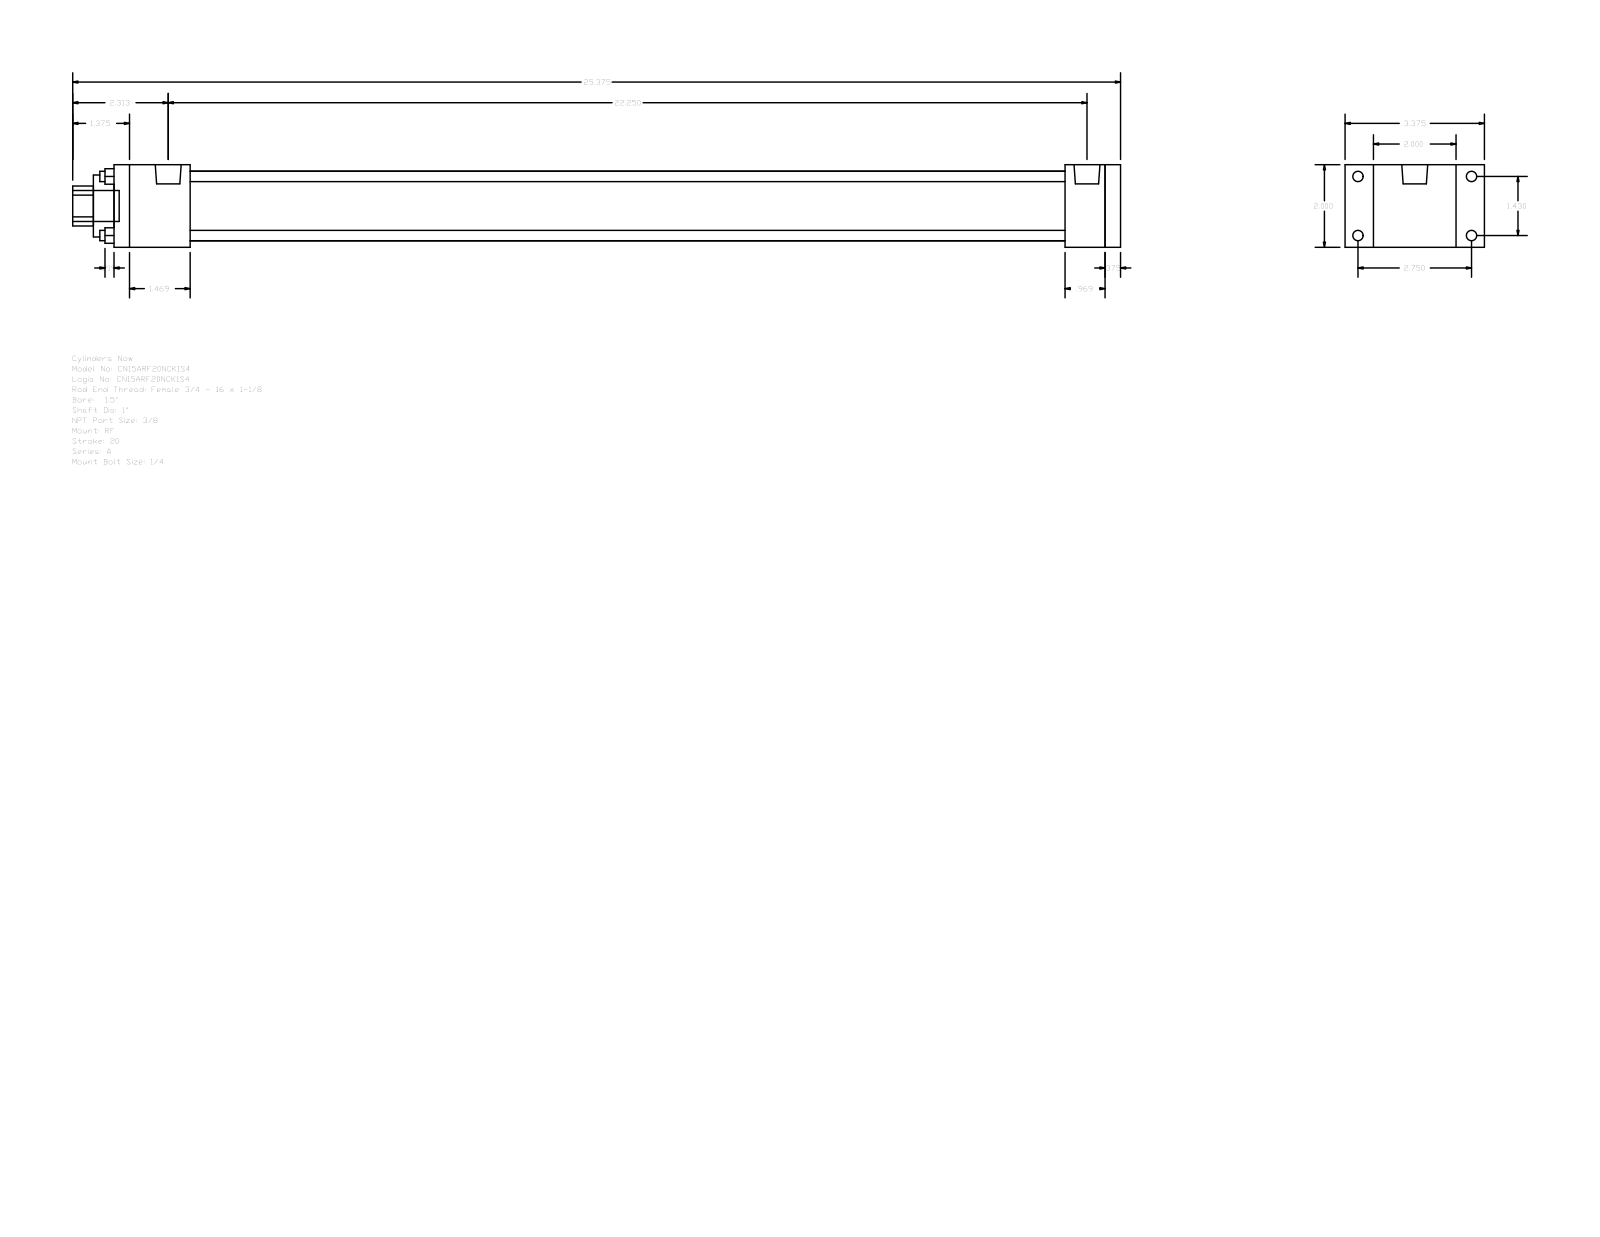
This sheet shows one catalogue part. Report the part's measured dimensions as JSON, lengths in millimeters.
{"part_name": "A_RF__0150_1", "step_written_by": "GSSL Pune (CONFIG_CONTROL_DESIGN)", "units": "millimeters", "bodies": {"solids": 0, "faces": 92, "planar": 64, "cylindrical": 28, "other": 0}, "overall_size": [644.52, 85.72, 50.8], "round_holes": [[6.35, 4], [25.4, 1], [38.1, 1], [42.93, 1]], "round_bosses_or_shafts": [[6.35, 4], [5.56, 4], [15.93, 2], [19.05, 1]], "partial_cylinders_radius": [[12.29, 1]], "face_to_face_distances": [50.8, 9.52, 609.6, 619.12, 584.99, 24.61, 34.13, 46.83, 538.16, 562.77], "hole_center_spacings": [25.68, 36.32, 51.36]}
